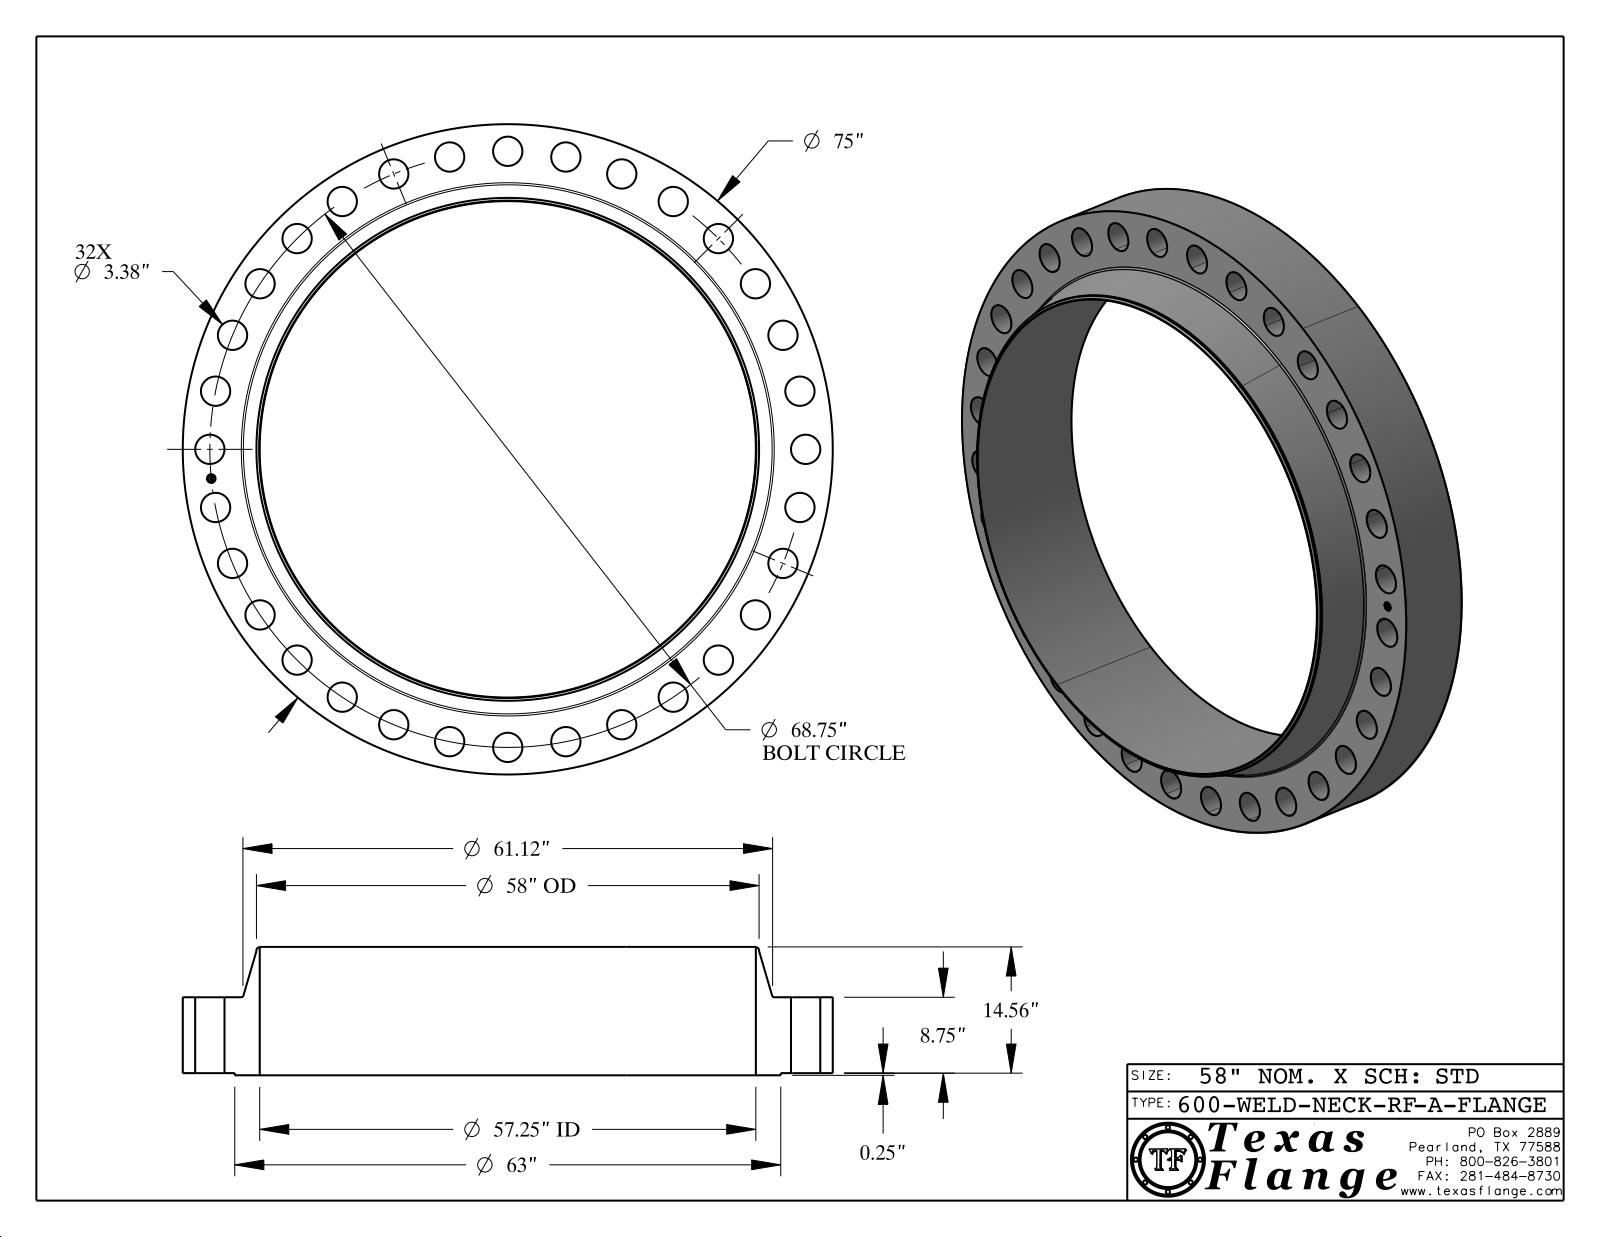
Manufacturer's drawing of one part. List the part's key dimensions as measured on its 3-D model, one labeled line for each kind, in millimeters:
Part name (STEP PRODUCT): 600-WELD-NECK-RF, Series A
STEP written by: CATIA V5 STEP AP214 (AUTOMOTIVE_DESIGN)
Units: millimetres
Bodies: 1 solid, 467 faces (369 planar, 92 cylindrical, 6 other)
Overall size (bounding box): 1905 × 1905 × 376.2
Volume: 244 400 000 mm³ · Surface area: 7 521 000 mm²
Round holes (diameter × count): ⌀85.9 ×32, ⌀25.4 ×1, ⌀1454.2 ×1
Round bosses / shafts (diameter × count): ⌀1.5 ×8, ⌀1905 ×1, ⌀1600.2 ×1, ⌀1473.2 ×1, ⌀20 ×1
Main face-to-face distances: 222.3, 6.4, 228.6, 376.2, 369.8, 147.6, 0.4, 228.2, 221.9, 148
Hole centre spacings: 506.9, 668.2, 1671.1, 1349.9, 1737.8, 1540.1, 171.2, 1107.8
